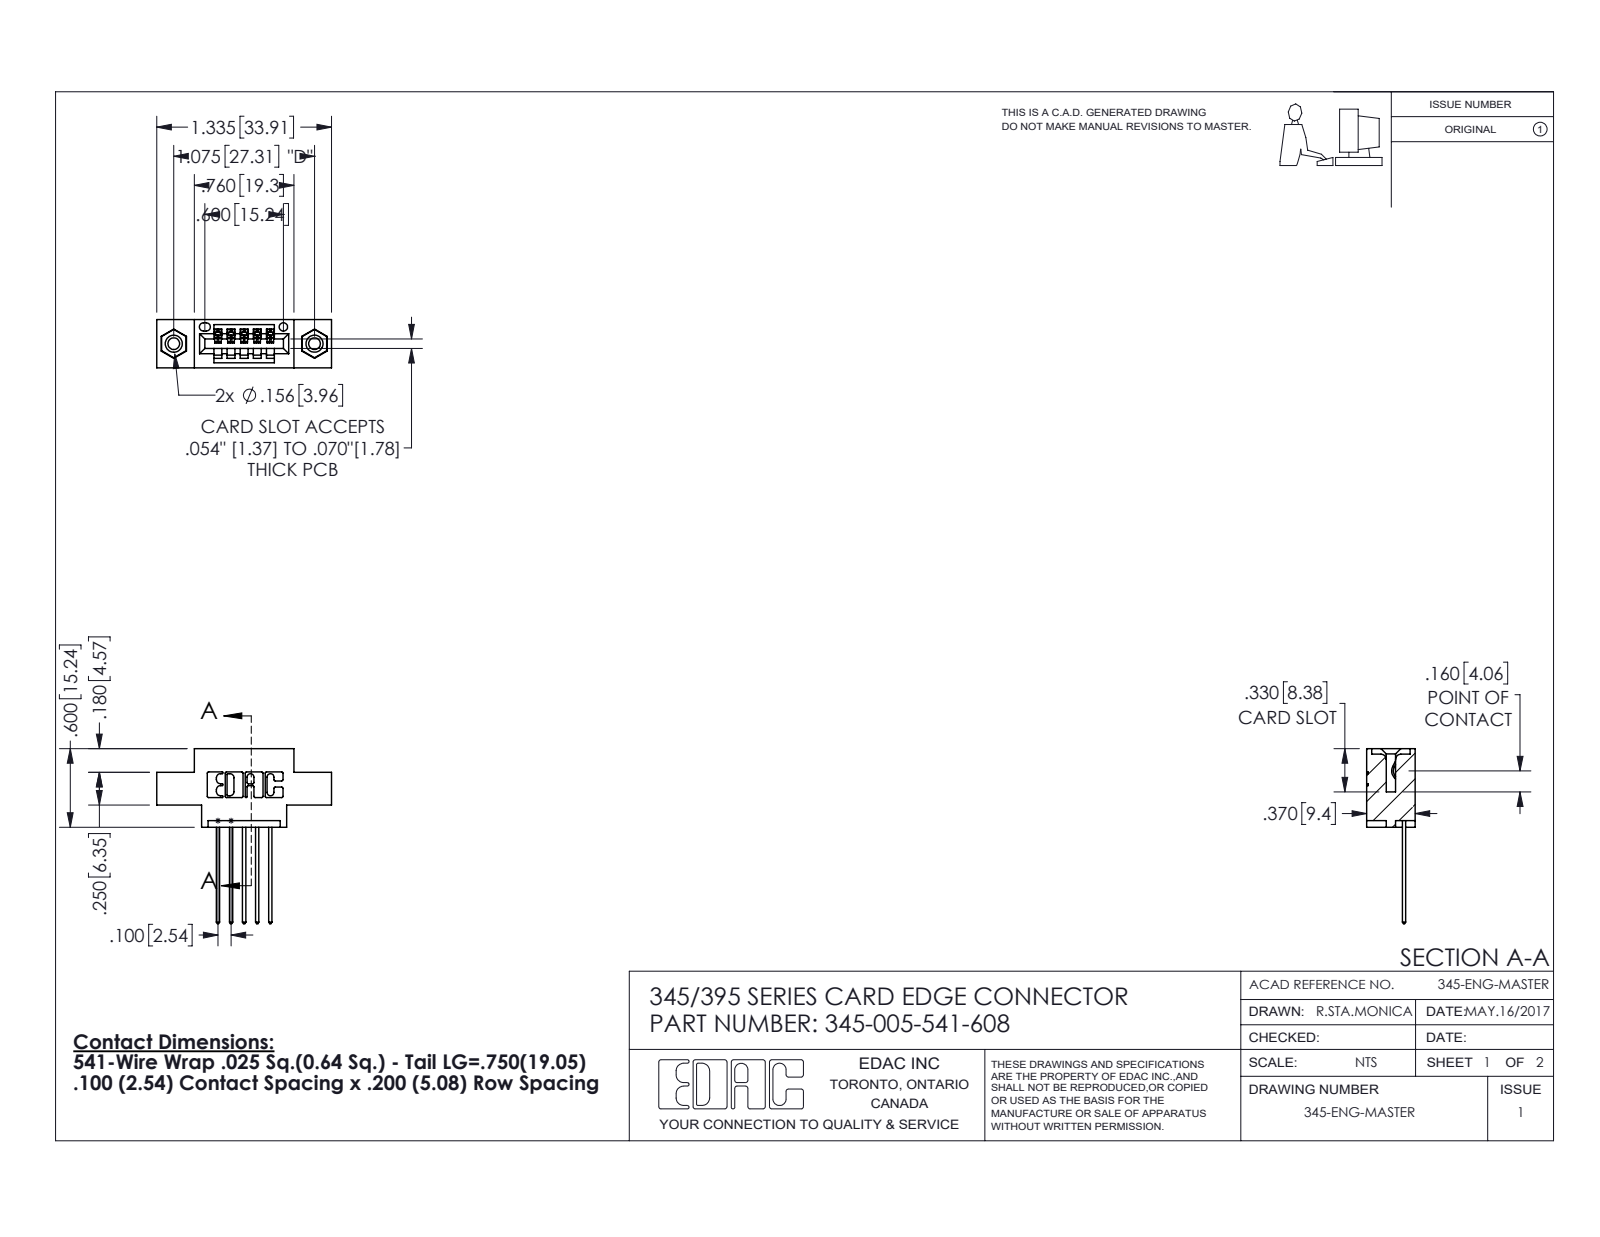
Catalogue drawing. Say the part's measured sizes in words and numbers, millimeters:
The part is named "345-250-001_345-250-003-102; 345 Part_0.170 Offset - 0.156 Dia-TI; 345-005-541-608; 345-292-001_345-293-141". Its 3-D file was written by "SolidWorks 2016 (CONFIG_CONTROL_DESIGN)". It is 8 solids with 480 faces: 316 planar, 148 cylindrical and 16 other. Overall it measures 34 by 33.9 by 9.4 millimeters. Its volume is 2 820 cubic millimeters and its surface area 3 480 square millimeters. Round holes: 2 of diameter 2.3, 2 of diameter 3.2, 2 of diameter 4, 1 of diameter 1.6. Round bosses or shafts: 2 of diameter 3.9. Partial cylindrical surfaces (rounded edges, fillets, slot ends): 22 of radius 0.3, 10 of radius 0.2, 10 of radius 0.3, 6 of radius 0.2, 6 of radius 0.8, 3 of radius 0.7, 2 of radius 0.8, 2 of radius 1. The main face-to-face distances are 9.4, 5.1, 1.8, 7.6, 2.5, 0.6, 2.5, 6.9, 6.4, 1.5. The hole center spacings are 6.9, 21.5, 27.3.
